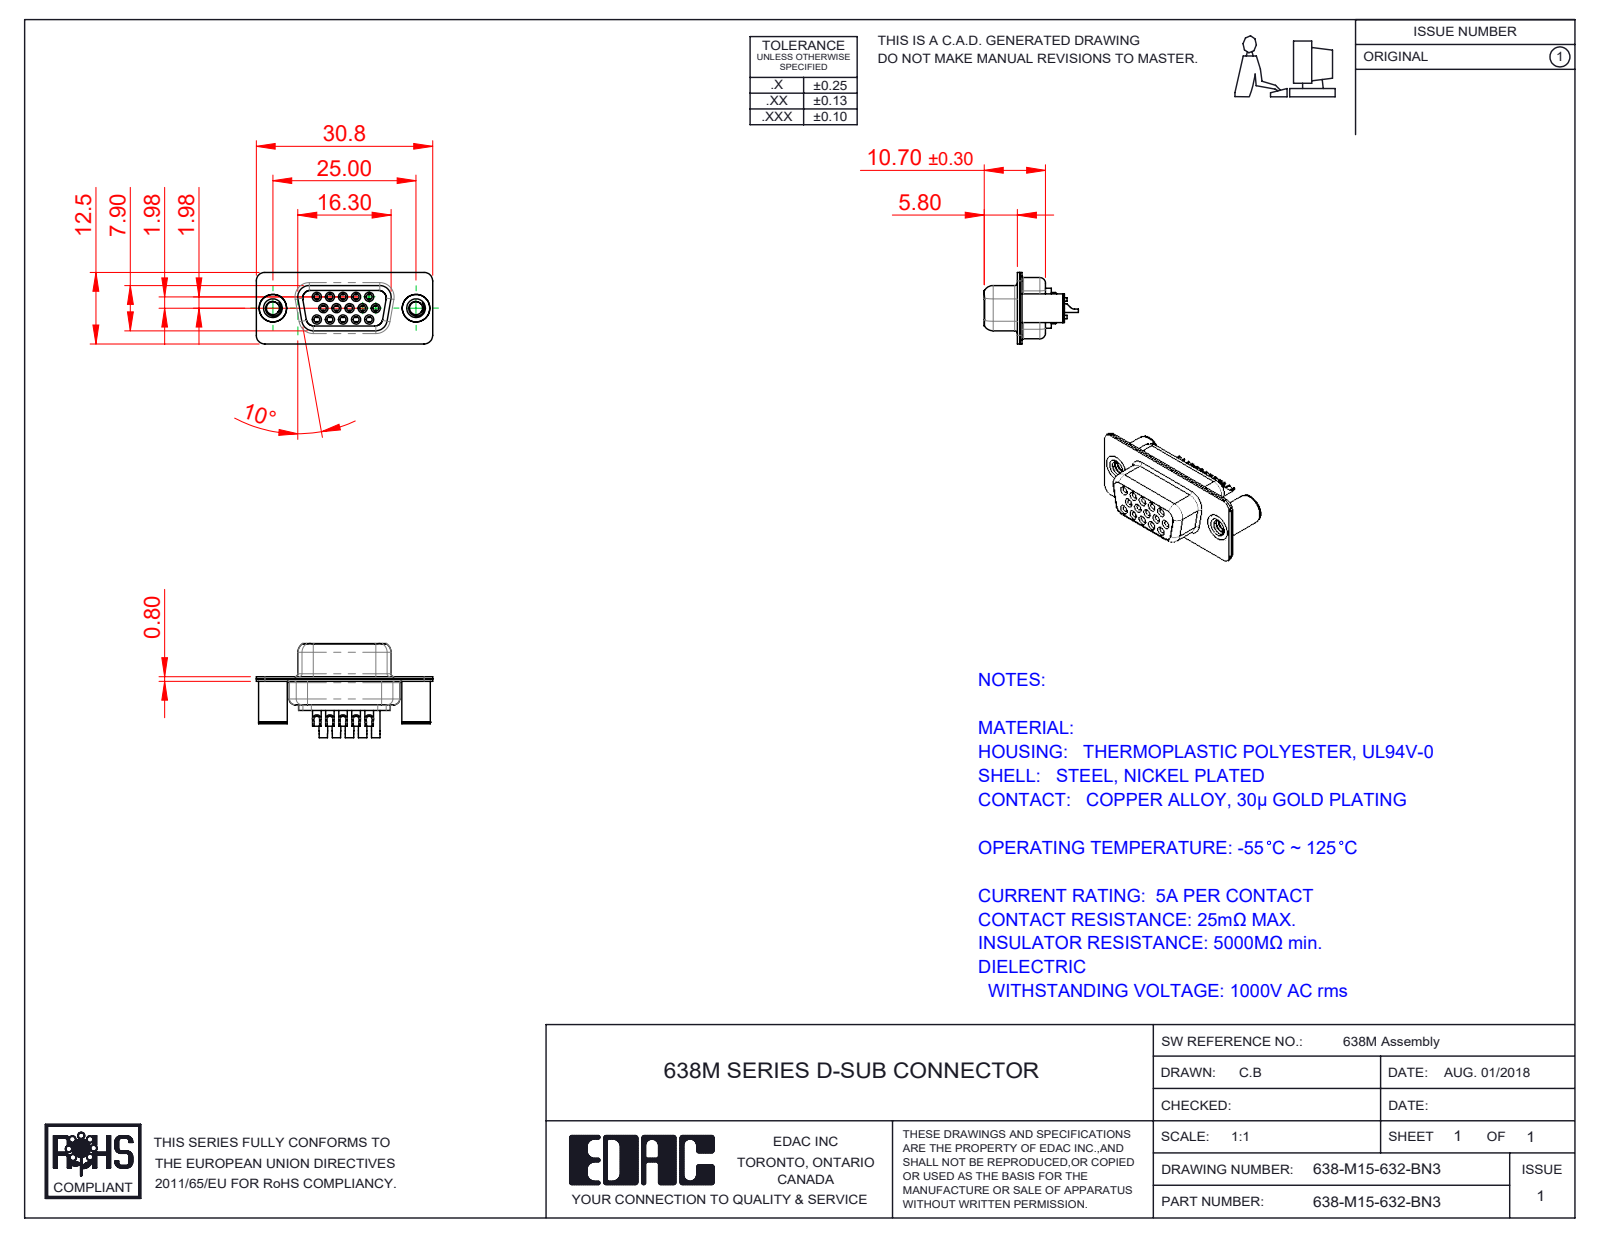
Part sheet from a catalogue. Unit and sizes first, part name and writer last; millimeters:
Units: millimetres
Overall size (bounding box): 30.8 × 16.45 × 12.5
Round holes (diameter × count): ⌀1 ×16, ⌀1.1 ×15, ⌀1.7 ×15, ⌀1.8 ×15, ⌀2 ×15, ⌀2.26 ×2, ⌀3.26 ×2, ⌀4 ×2, ⌀4.8 ×2
Round bosses / shafts (diameter × count): ⌀2.2 ×15, ⌀1.6 ×15, ⌀1.5 ×15, ⌀5 ×2, ⌀4.9 ×2
Partial cylindrical surfaces — rounded edges, fillets, slot ends (radius × count): R1.5 ×16, R2 ×12, R1.35 ×8, R1.6 ×8, R1 ×7, R0.25 ×4, R0.5 ×4, R0.6 ×4
Main face-to-face distances: 0.4, 1.4, 0.45, 8.45, 0.8, 8.9, 1, 1.8, 6.2, 7.05
Hole centre spacings: 2.28, 3.96, 2.29, 4.57, 6.05, 6.04, 6.86, 7.92
Volume: 1 782 mm³ · Surface area: 5 691 mm²
Bodies: 20 solids, 1138 faces (322 planar, 476 cylindrical, 340 other)
Part name (STEP PRODUCT): 638M Contact Row 3_32; 638-M15-632-BN3; 638M Contact Row 1_32; 638M 4-40 Threaded Board Spacer (+4 more)
STEP written by: SolidWorks 2020 (CONFIG_CONTROL_DESIGN)
